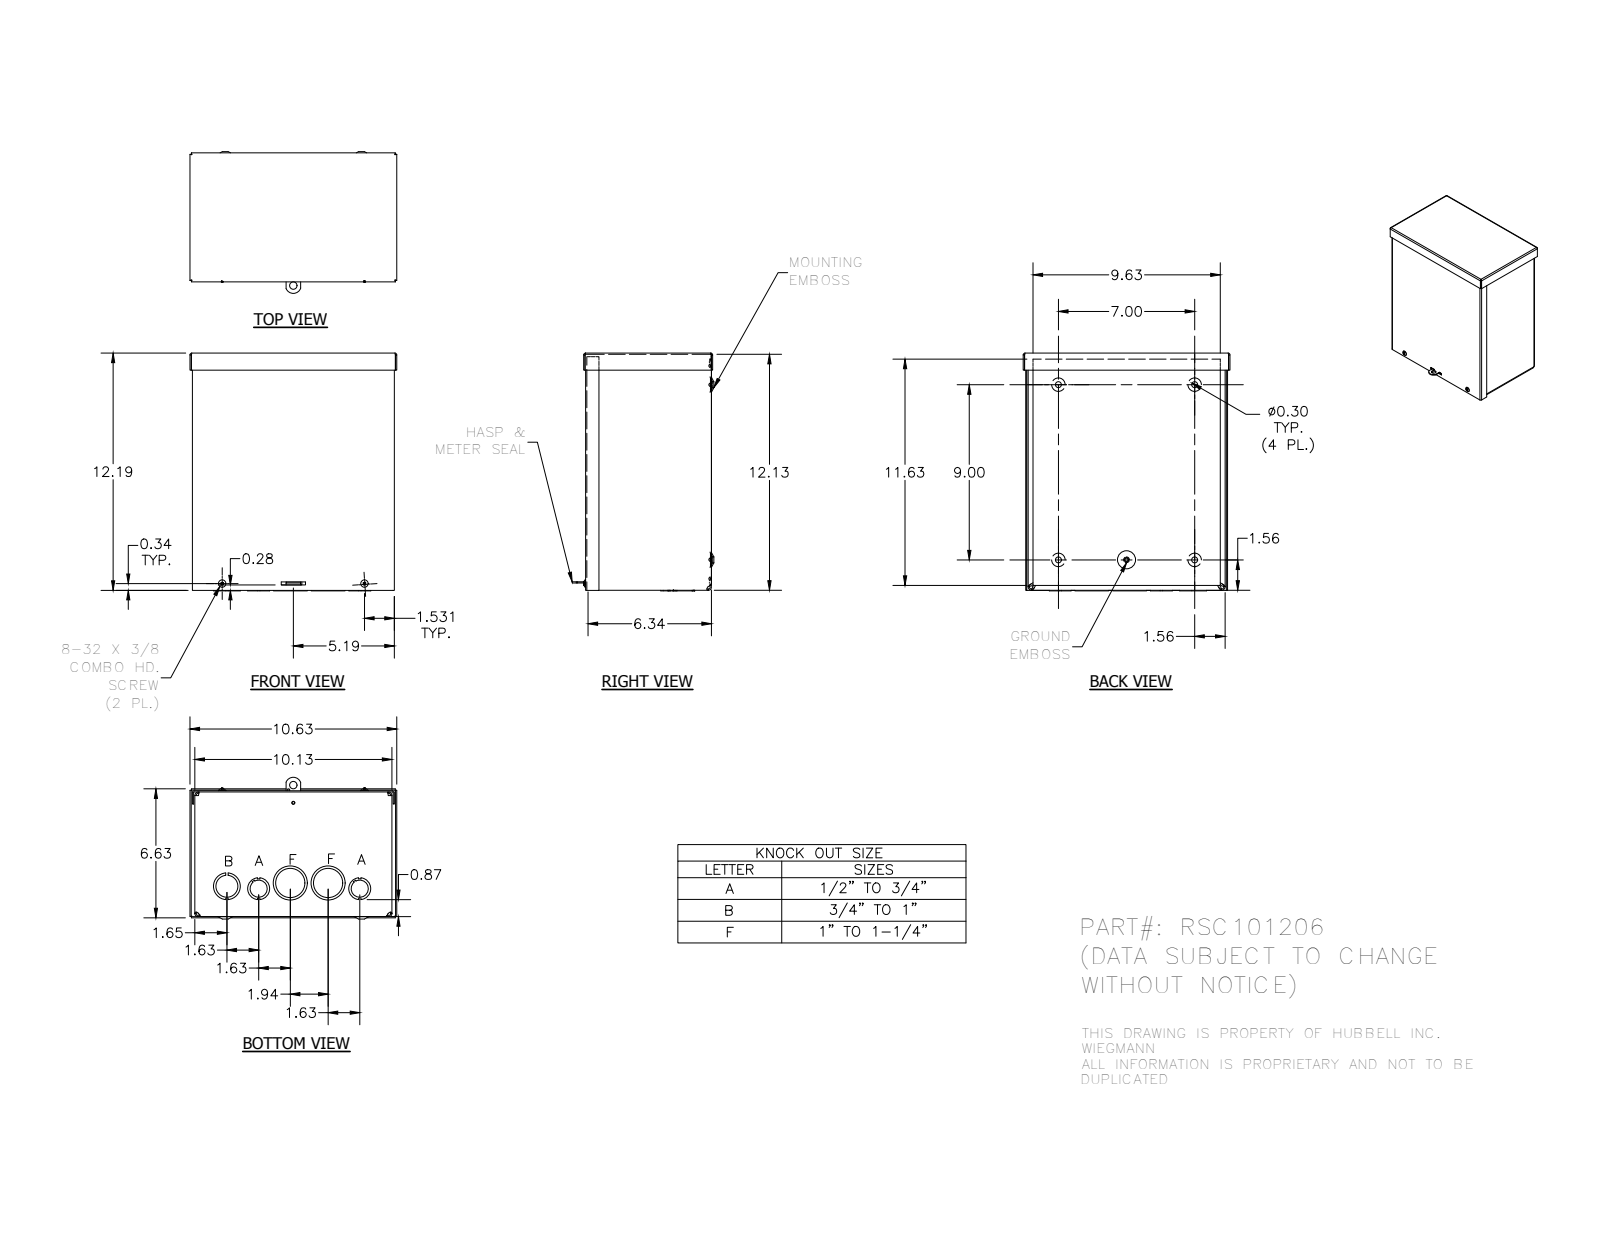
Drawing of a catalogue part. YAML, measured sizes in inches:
part_name: "RSC101206; RSC101206_WRAP; RSC1012_LID; RSC1006_CAP (+4 more)"
step_written_by: "Autodesk Inventor 2012 (AUTOMOTIVE_DESIGN)"
units: inches
bodies: {solids: 7, faces: 518, planar: 245, cylindrical: 129, other: 144}
overall_size: [12.281, 10.625, 7.125]
volume: 42.49
surface_area: 1388
round_holes:
  - {diameter: 0.3, count: 4}
  - {diameter: 0.313, count: 4}
  - {diameter: 1.125, count: 3}
  - {diameter: 0.125, count: 2}
  - {diameter: 0.148, count: 2}
  - {diameter: 0.875, count: 2}
  - {diameter: 1.5, count: 2}
  - {diameter: 1.75, count: 2}
  - {diameter: 0.156, count: 1}
  - {diameter: 0.165, count: 1}
  - {diameter: 0.375, count: 1}
  - {diameter: 1.375, count: 1}
round_bosses_or_shafts:
  - {diameter: 0.384, count: 2}
  - {diameter: 0.164, count: 2}
  - {diameter: 0.229, count: 1}
partial_cylinders:
  - {radius: 0.01, count: 10}
  - {radius: 0.031, count: 8}
  - {radius: 0.093, count: 8}
  - {radius: 0.125, count: 8}
  - {radius: 0.187, count: 8}
  - {radius: 0.031, count: 4}
  - {radius: 0.055, count: 4}
  - {radius: 0.062, count: 4}
face_to_face_distances: [0.062, 0.062, 10.126, 6.249, 6.187, 0.063, 12.126, 6.312, 6.25, 0.124]
hole_center_spacings: [1.072, 1.261, 1.656, 3.5, 3.582, 7, 7.313, 9]
